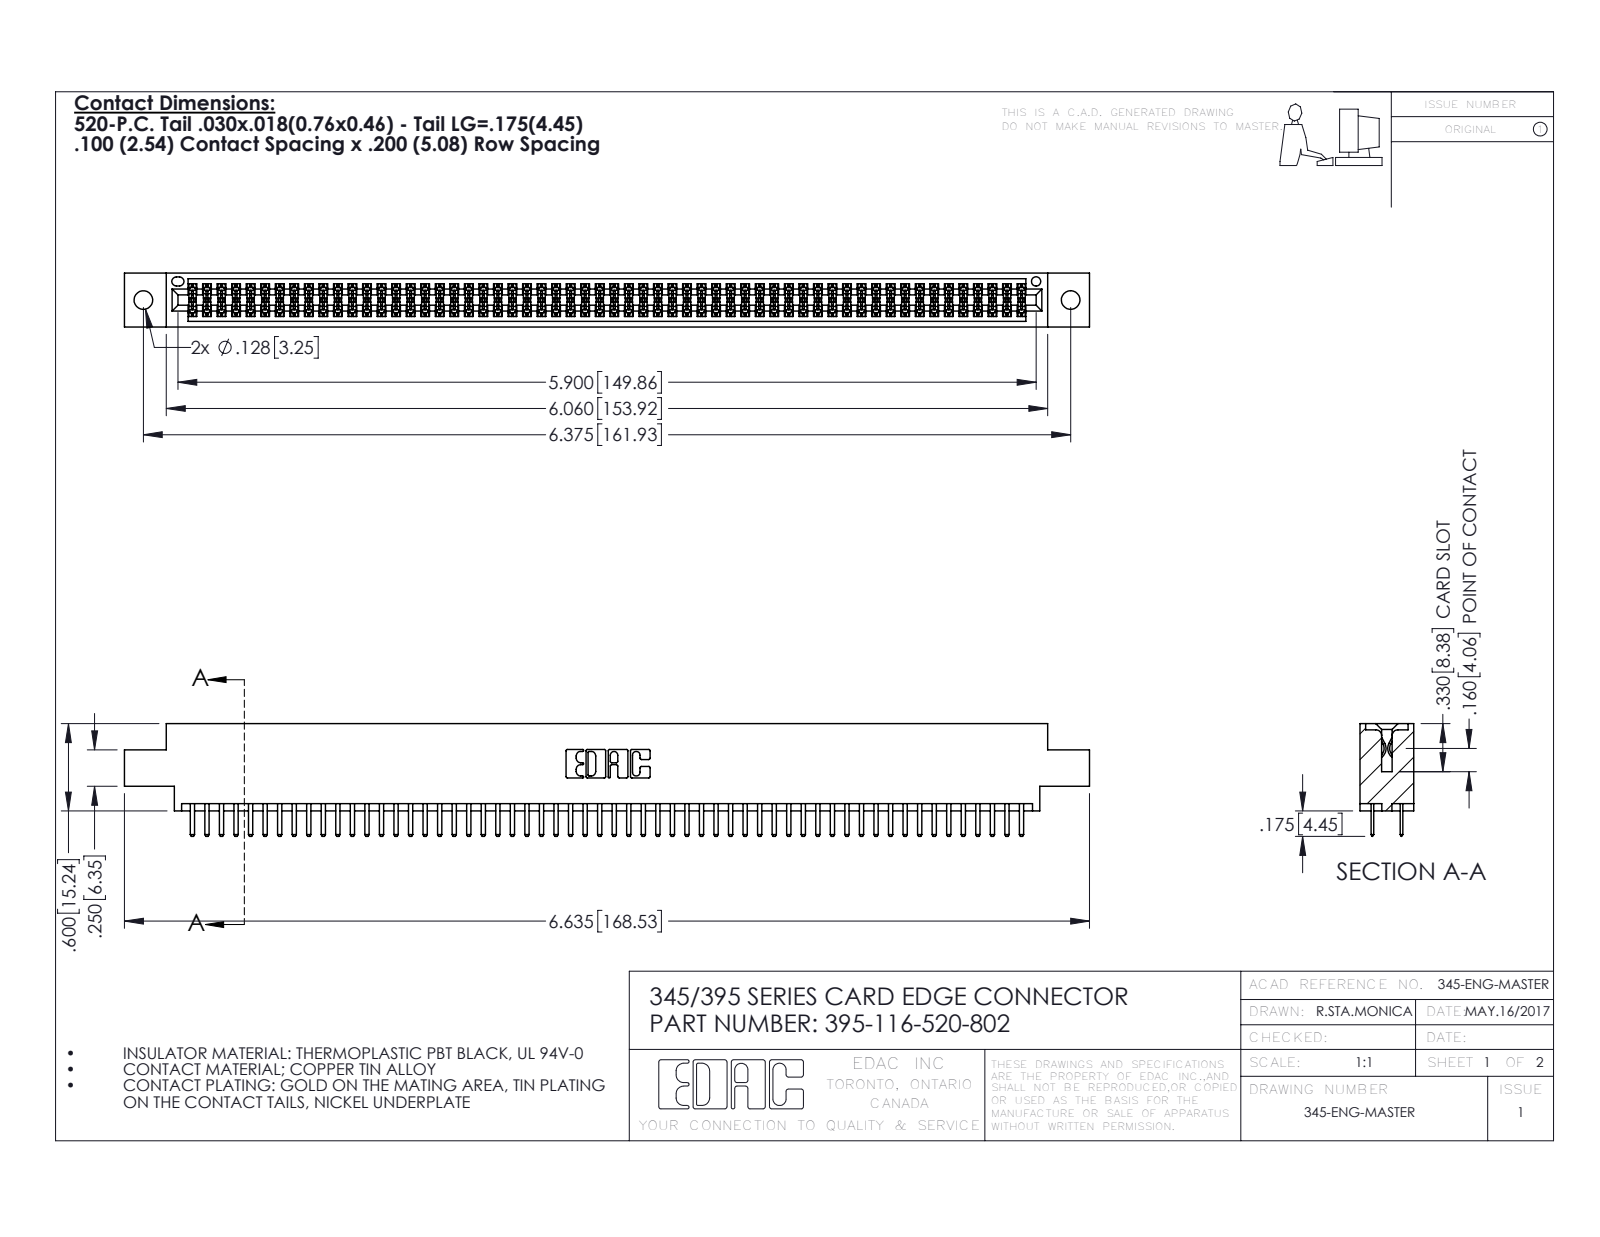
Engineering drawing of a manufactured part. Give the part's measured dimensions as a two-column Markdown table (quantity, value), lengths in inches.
| quantity | value |
| --- | --- |
| part name | 345-292-001_345-293-120; 395-116-520-802; 345 Part_0.170 Offset - 0.128 Dia |
| STEP written by | SolidWorks 2016 (CONFIG_CONTROL_DESIGN) |
| units | inches |
| bodies | 117 solids, 6394 faces (4144 planar, 2250 cylindrical, 0 other) |
| overall size | 6.635 × 0.775 × 0.37 |
| volume | 0.996 in³ |
| surface area | 37.5 in² |
| round holes (diameter × count) | 0.128 × 2, 0.064 × 1 |
| partial cylindrical surfaces (radius × count) | 0.006 × 174, 0.01 × 120, 0.01 × 22, 0.007 × 6, 0.031 × 6, 0.026 × 3, 0.014 × 2, 0.019 × 2 |
| main face-to-face distances | 0.298, 0.072, 0.2, 0.37, 0.098, 0.272, 0.025, 0.225, 0.022, 0.072 |
| hole center spacings | 0.27, 6.139, 6.375 |
